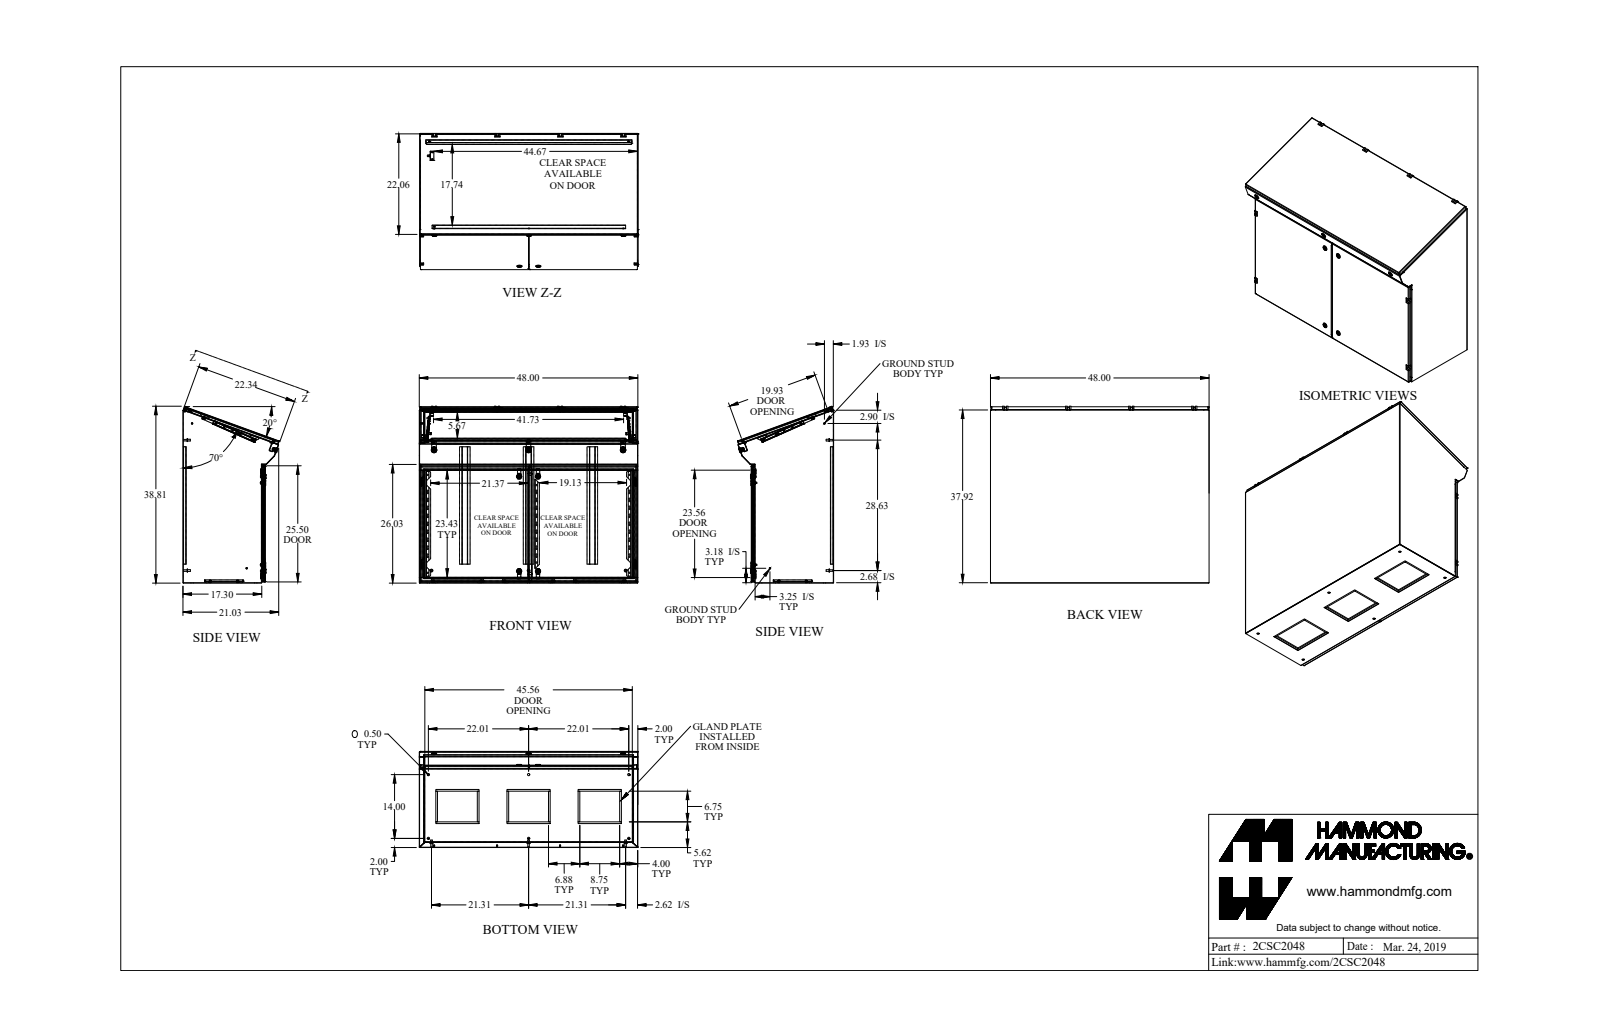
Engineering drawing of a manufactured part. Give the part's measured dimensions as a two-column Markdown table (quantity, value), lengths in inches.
| quantity | value |
| --- | --- |
| part name | 2CSC2048 |
| STEP written by | SolidWorks 2018 (AUTOMOTIVE_DESIGN) |
| units | inches |
| bodies | 157 solids, 3127 faces (2204 planar, 733 cylindrical, 190 other) |
| overall size | 48 × 38.809 × 21.099 |
| volume | 639 in³ |
| surface area | 16 444 in² |
| round holes (diameter × count) | 0.281 × 68, 0.5 × 13, 0.196 × 12, 0.189 × 8, 0.197 × 8, 0.313 × 8, 0.197 × 7, 0.387 × 7, 0.63 × 7, 0.768 × 7, 0.391 × 4, 0.25 × 3 |
| round bosses / shafts (diameter × count) | 0.236 × 19, 0.25 × 17, 0.236 × 15, 0.313 × 10, 0.374 × 8, 1.1 × 7, 0.625 × 7, 0.65 × 6 |
| partial cylindrical surfaces (radius × count) | 0.036 × 60, 0.108 × 60, 0.125 × 48, 0.043 × 12, 0.116 × 12, 0.188 × 12, 0.25 × 12, 0.047 × 8 |
| main face-to-face distances | 0.072, 0.072, 17.943, 18.015, 18.087, 18.015, 47.856, 47.928, 47.928, 48 |
| hole center spacings | 1.75, 3.5, 5.25, 10.5, 7, 8.75, 20.753, 20.753 |
